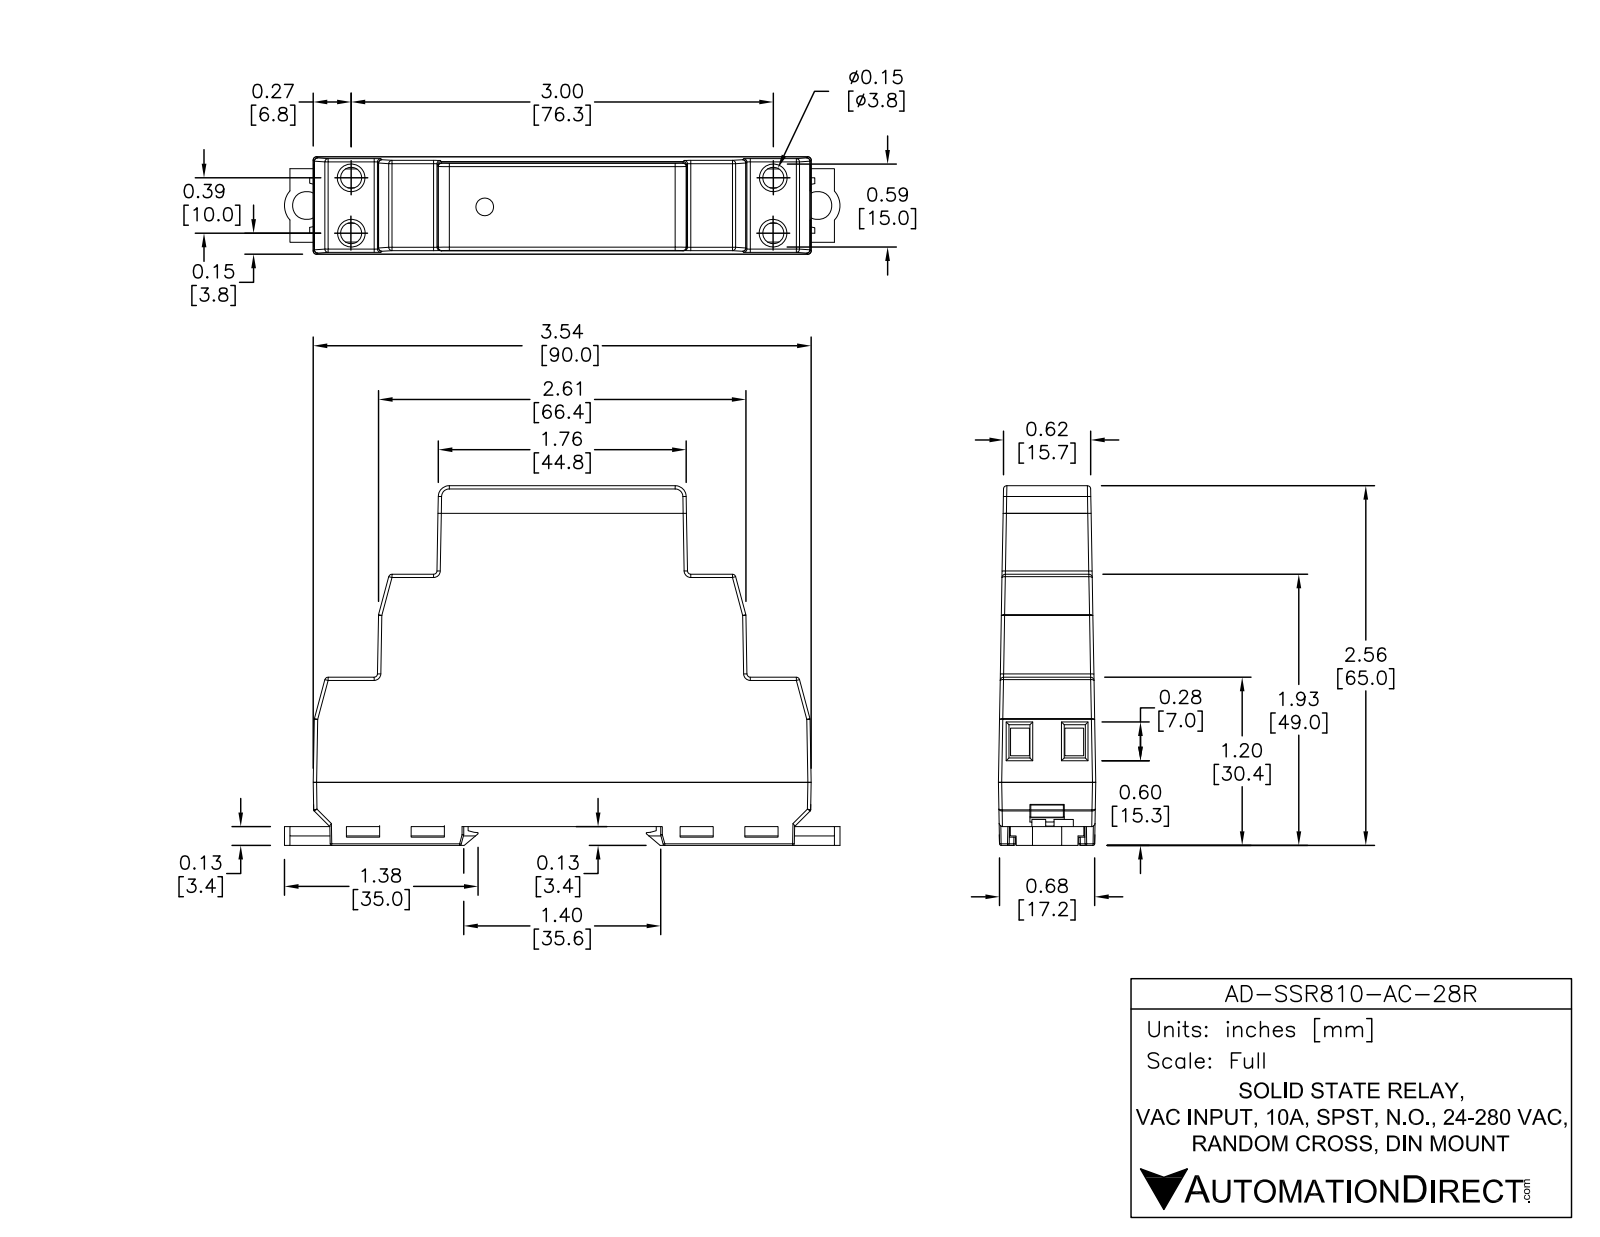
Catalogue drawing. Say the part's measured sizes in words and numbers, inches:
The part is named "AD-SSR810-AC-28R". Its 3-D file was written by "SolidWorks 2013 (AUTOMOTIVE_DESIGN)". It is 1 solid with 843 faces: 495 planar, 78 cylindrical and 270 other. Overall it measures 3.924 by 2.616 by 0.685 inches. Its volume is 4.605 cubic inches and its surface area 24.23 square inches. Round holes: 4 of diameter 0.19, 2 of diameter 0.2. Round bosses or shafts: 1 of diameter 0.105. Partial cylindrical surfaces (rounded edges, fillets, slot ends): 41 of radius 0.015, 2 of radius 0.06, 2 of radius 0.172. The main face-to-face distances are 2.525, 0.049, 2.574, 0.425, 2.215, 0.025, 0.05, 1.934, 1.885, 0.64. The hole center spacings are 0.338, 3.3, 0.364, 3.01, 3.032, 3.58.
